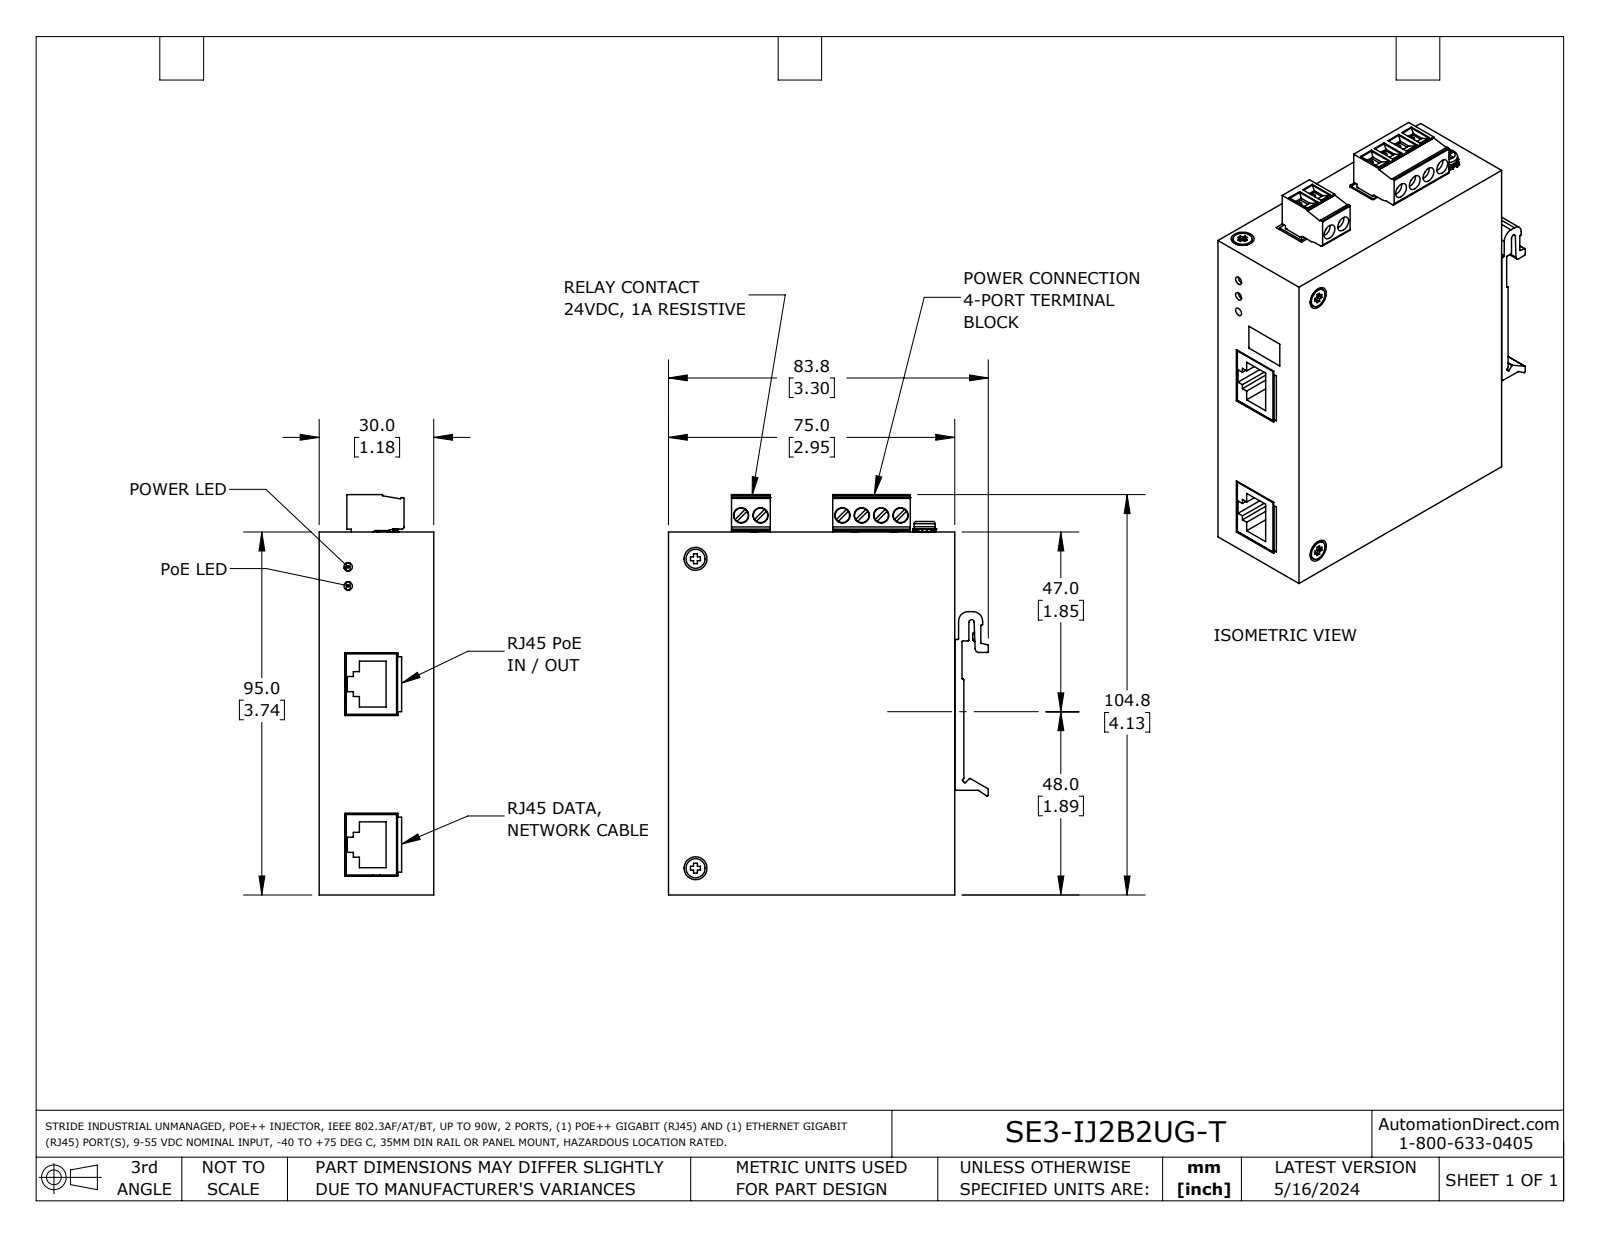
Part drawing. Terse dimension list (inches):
name: SE3-IJ2B2UG-T
written by: SolidWorks 2023 (AUTOMOTIVE_DESIGN)
unit: in
bodies: 24 solids, 1271 faces (855 planar, 278 cylindrical, 138 other)
size: 4.126 × 3.299 × 1.181
volume: 2.352 in³; area: 101.3 in²
holes: 9× ⌀0.157, 8× ⌀0.079, 6× ⌀0.055, 6× ⌀0.11, 4× ⌀0.118, 3× ⌀0.087, 2× ⌀0.091, 1× ⌀0.059
bosses: 9× ⌀0.197, 9× ⌀0.094, 6× ⌀0.149, 4× ⌀0.11, 2× ⌀0.055, 1× ⌀0.217, 1× ⌀0.114
rounds: 67× R0.004, 33× R0.008, 13× R0.02, 6× R0.115, 6× R0.118, 5× R0.012, 4× R0.034, 4× R0.039
face distances: 0.039, 1.142, 0.02, 1.102, 2.913, 1.181, 3.701, 1.122, 1.161, 2.953
hole spacings: 0.2, 0.4, 1.044, 1.244, 1.444, 0.394, 0.6, 0.197
